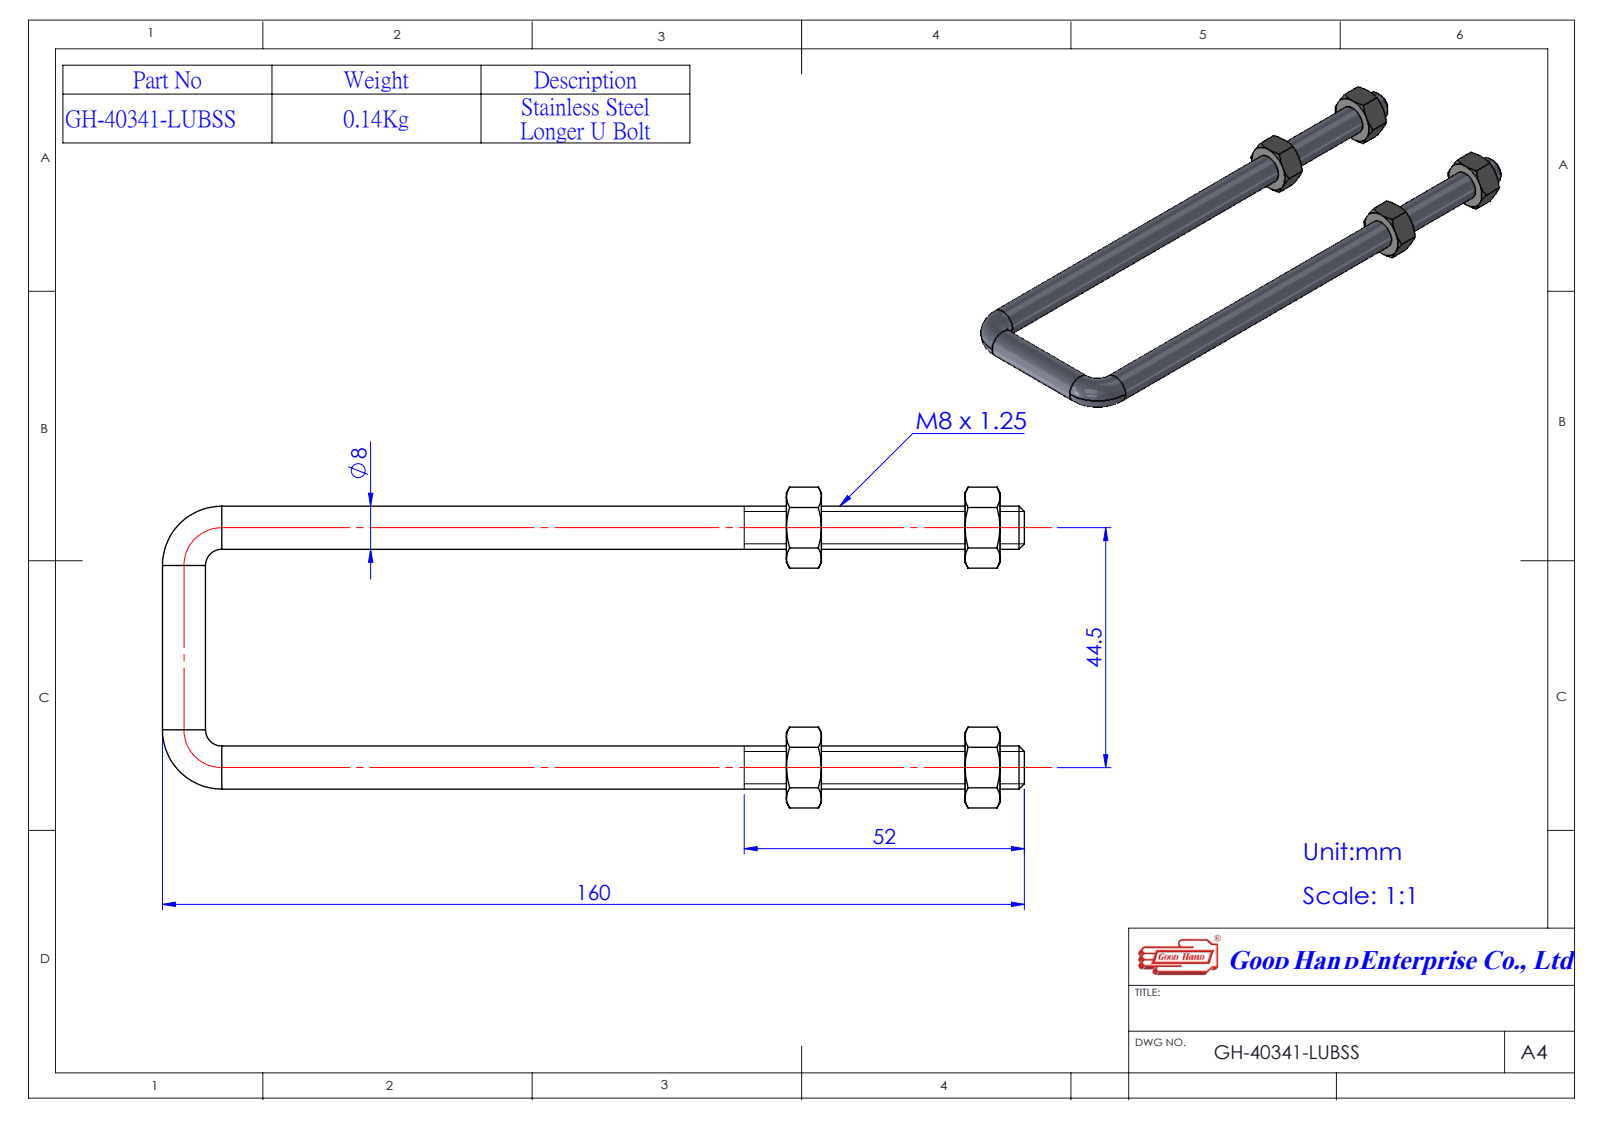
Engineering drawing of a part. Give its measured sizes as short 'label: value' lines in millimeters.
name: 14034144_160; GH-40341-LUBSS; Hexagon Nut_2_JIS_JIS B 1181 Hexagon nut - Class 2 Finished M8 --N
written by: SolidWorks 2016 (AUTOMOTIVE_DESIGN)
unit: mm
bodies: 5 solids, 132 faces (34 planar, 22 cylindrical, 76 other)
size: 160 × 59.51 × 13
volume: 20 412 mm³; area: 11 383 mm²
holes: 2× ⌀6.8, 2× ⌀8
bosses: 1× ⌀8
face distances: 13, 38.54, 33.15, 6.5, 51.54, 25.54, 39.65, 26.65, 44.17, 37.67
hole spacings: 44.5
